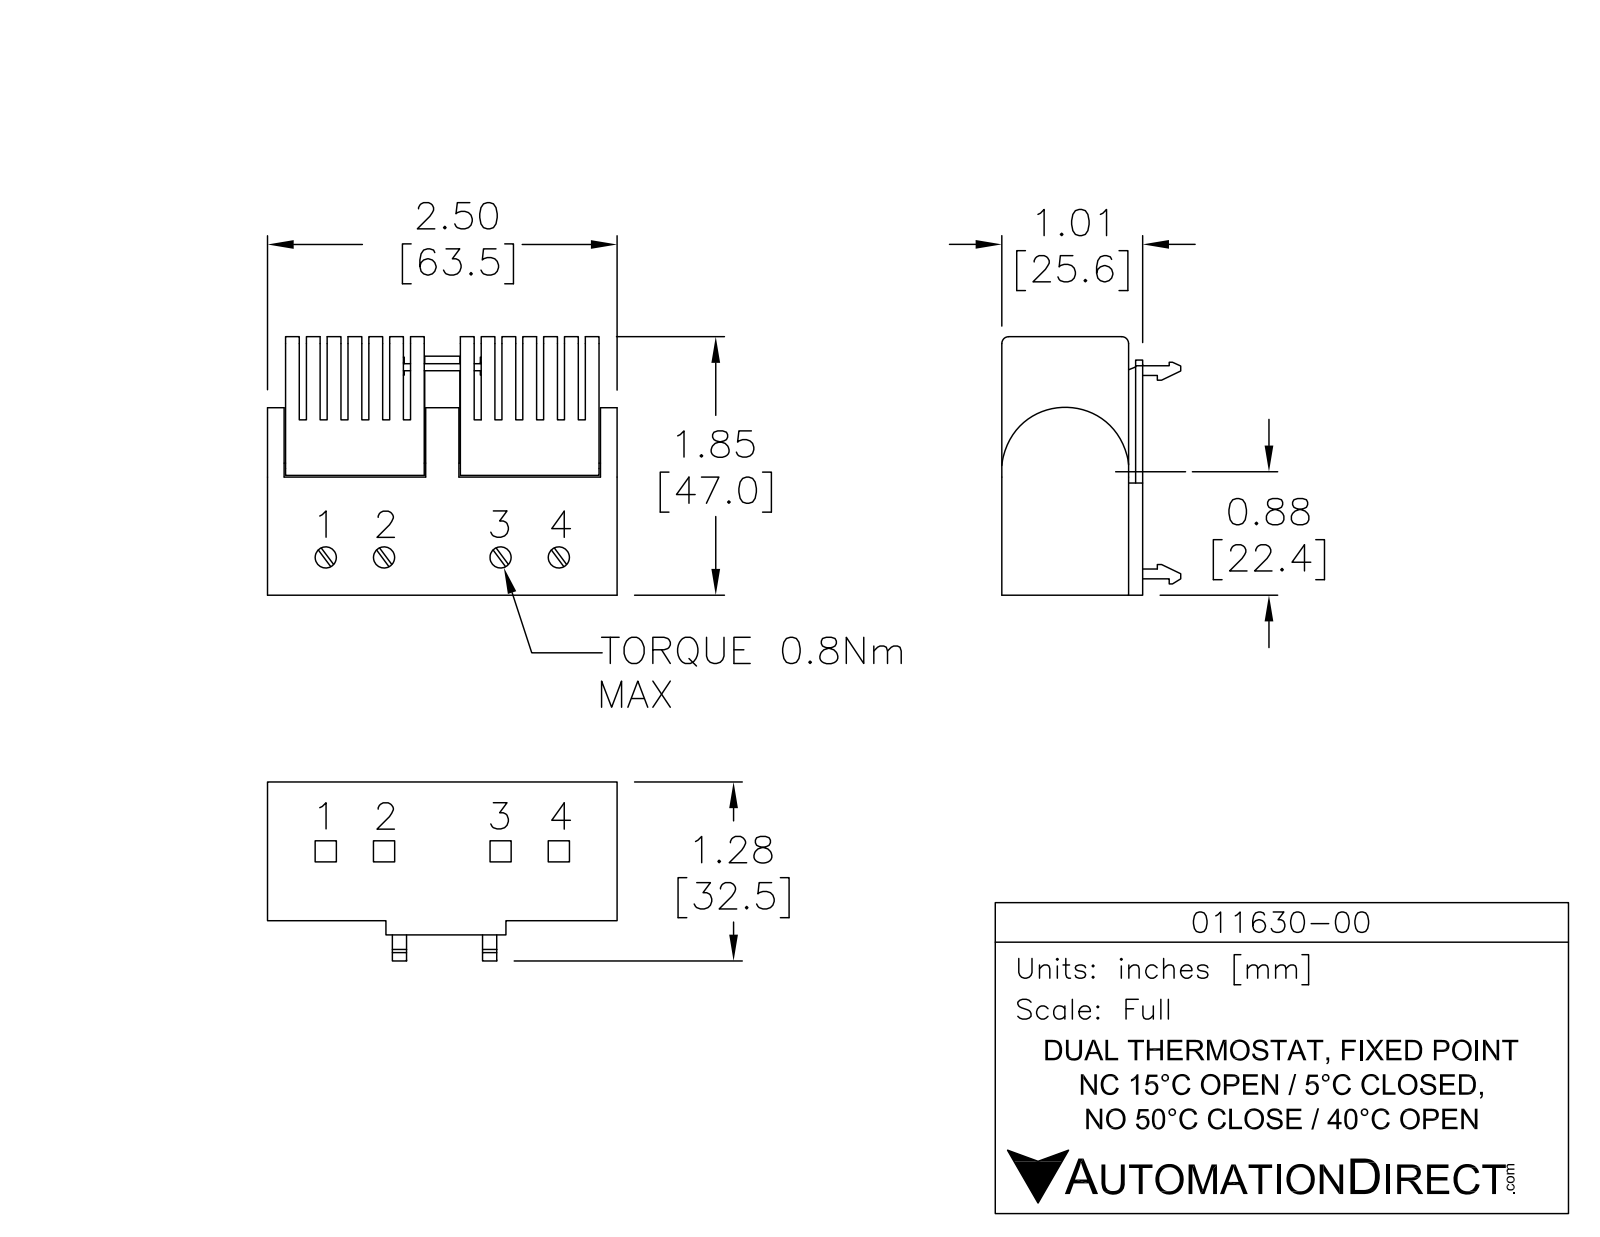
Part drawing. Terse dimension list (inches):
name: 011630-00
written by: SolidWorks 2013 (AUTOMOTIVE_DESIGN)
unit: in
bodies: 1 solid, 600 faces (292 planar, 212 cylindrical, 96 other)
size: 2.545 × 1.821 × 1.29
volume: 3.78 in³; area: 26.07 in²
rounds: 32× R0.025, 20× R0.023, 13× R0.03, 13× R0.06, 7× R0.015, 6× R0.04, 4× R0.486, 1× R0.452
face distances: 0.1, 2.545, 0.91, 0.911, 1.24, 1.24, 1.821, 0.03, 0.03, 0.178
